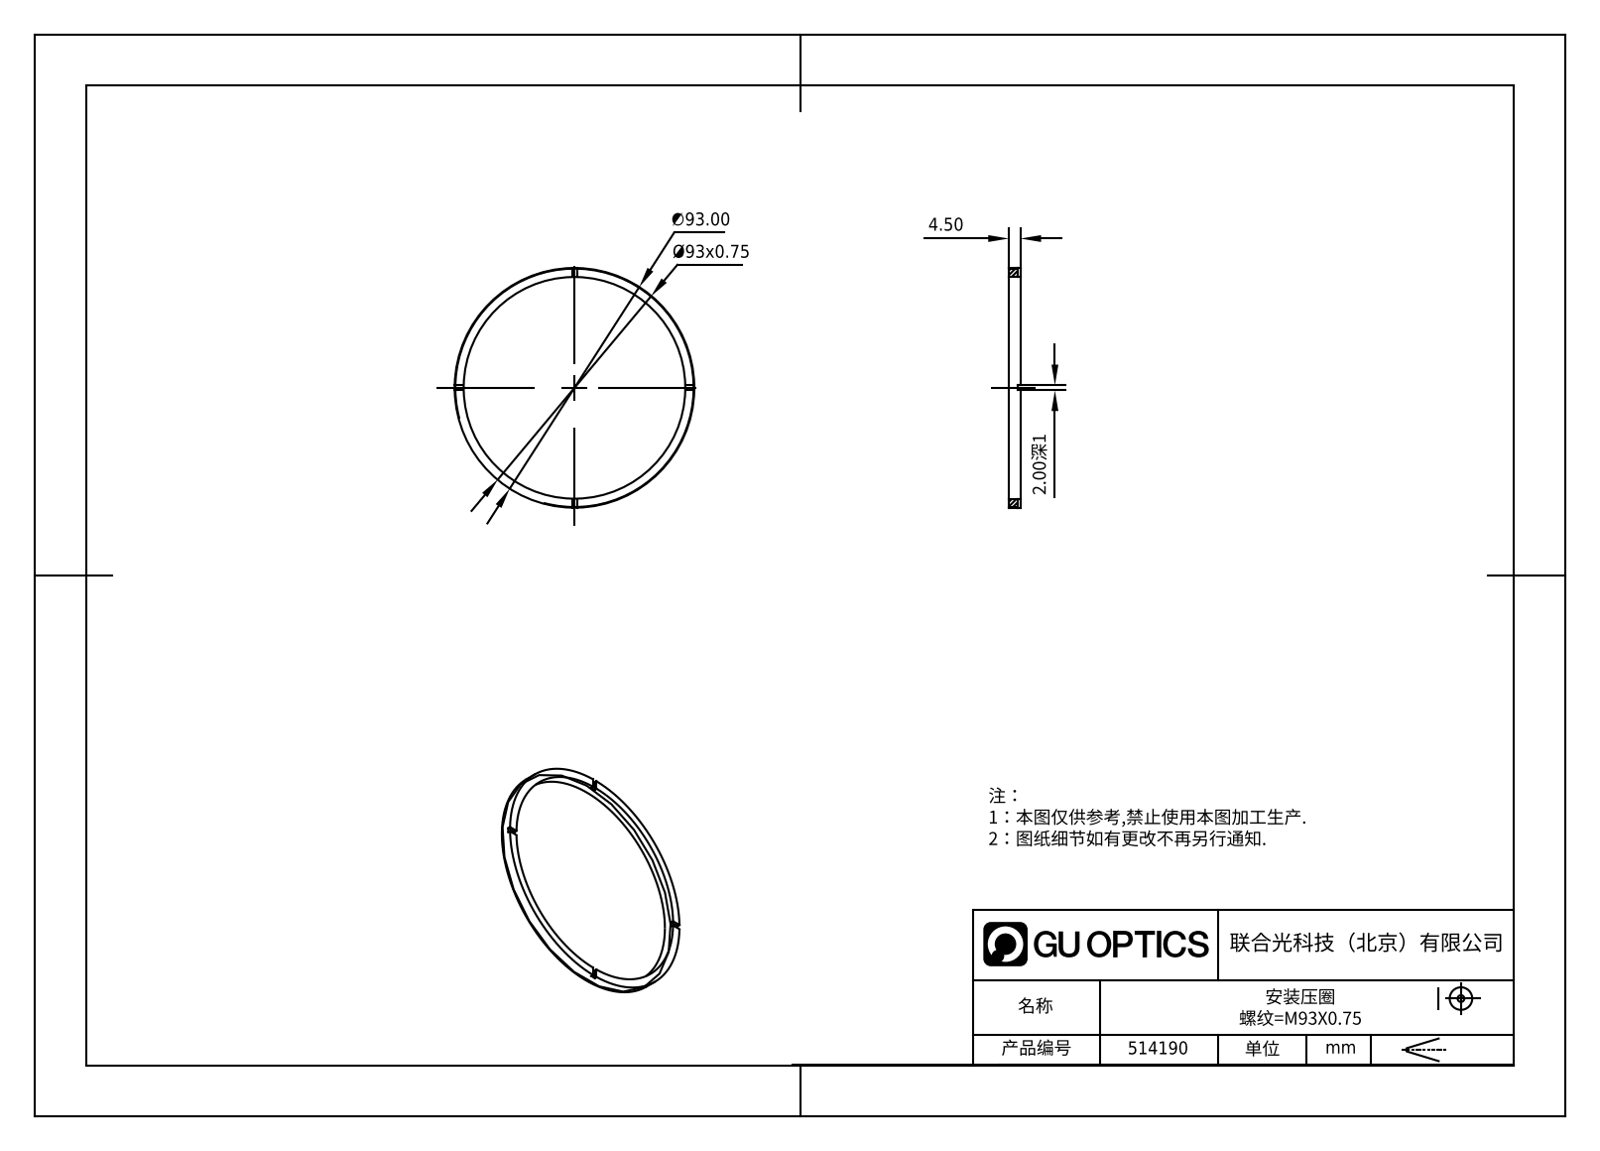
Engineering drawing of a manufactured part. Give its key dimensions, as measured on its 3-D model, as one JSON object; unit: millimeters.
{"part_name": "514190", "step_written_by": "SolidWorks 2020 (CONFIG_CONTROL_DESIGN)", "units": "millimeters", "bodies": {"solids": 1, "faces": 21, "planar": 17, "cylindrical": 4, "other": 0}, "overall_size": [93, 93, 4.5], "volume_mm3": 4400, "surface_area_mm2": 4511, "round_holes": [[86, 1]], "round_bosses_or_shafts": [[93, 1]], "face_to_face_distances": [4.5, 3.5, 1, 2]}
